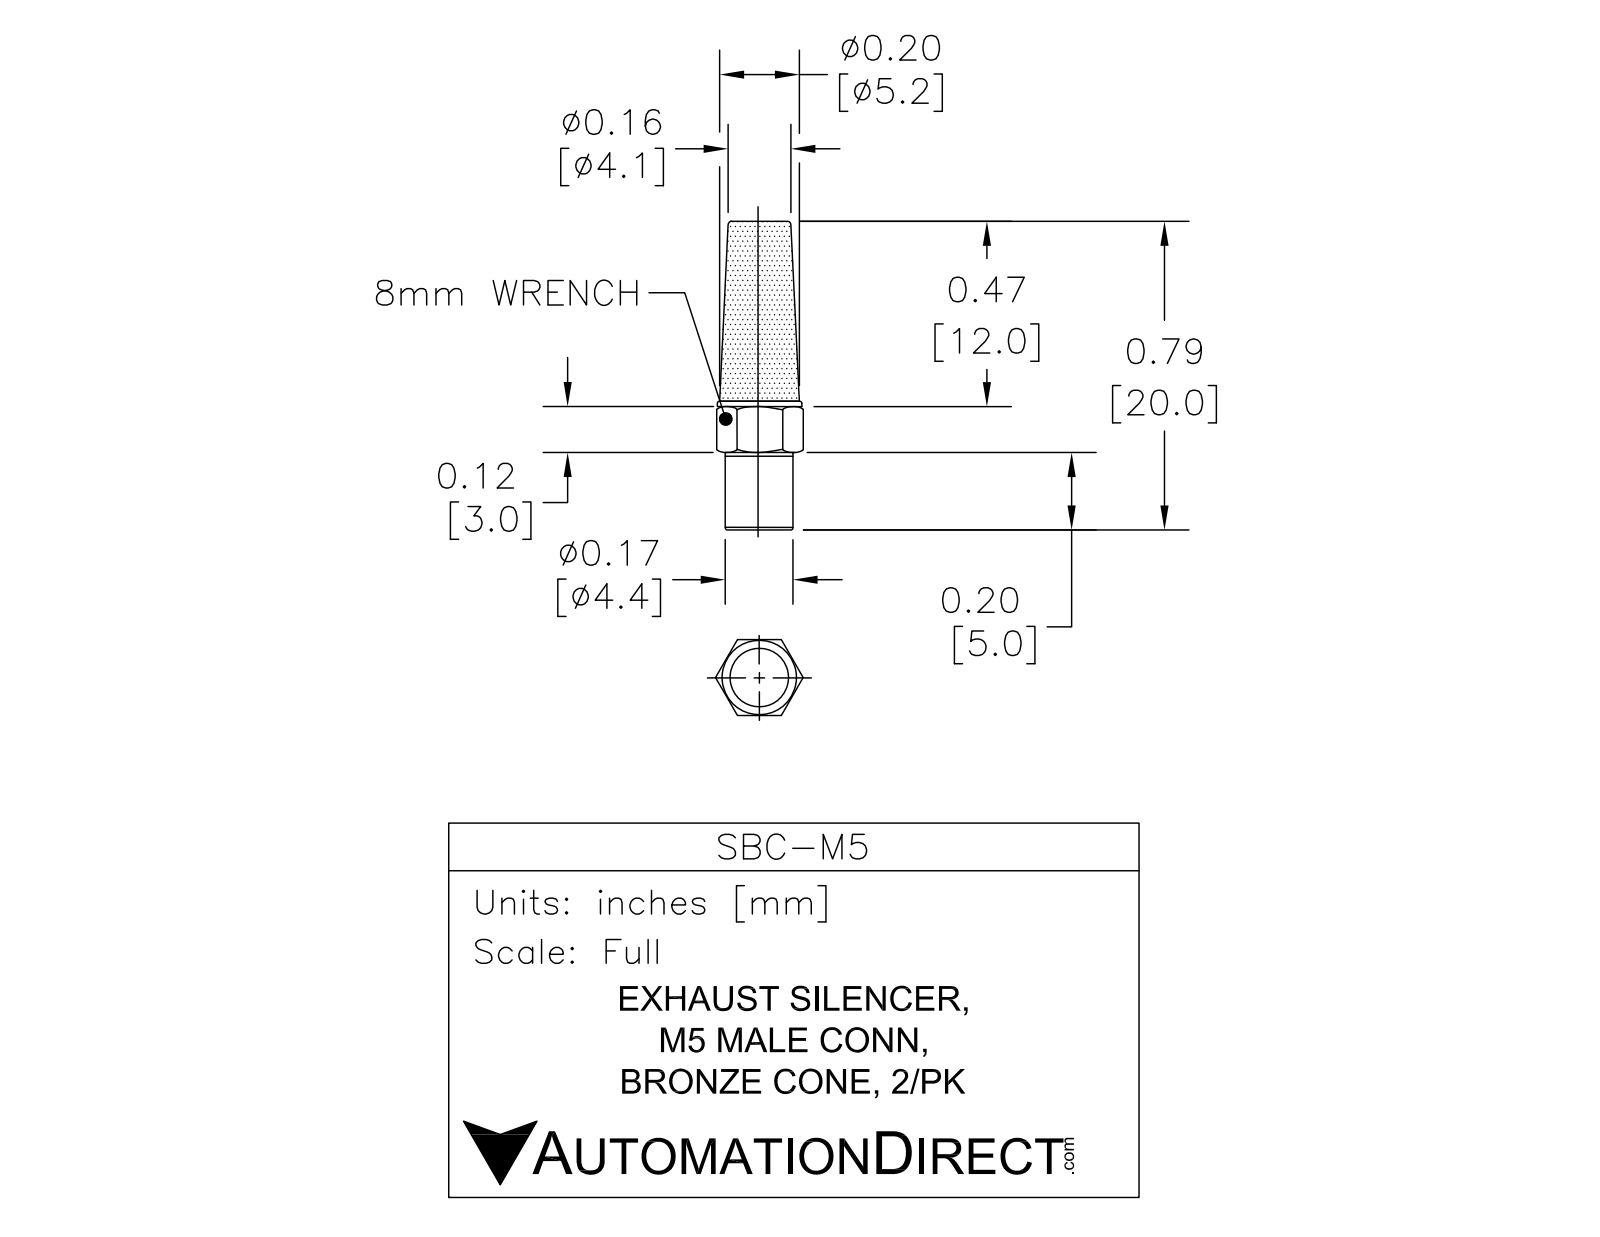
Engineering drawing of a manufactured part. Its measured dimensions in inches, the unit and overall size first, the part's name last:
Units: inches
Overall size (bounding box): 0.79 × 0.31 × 0.268
Round holes (diameter × count): ⌀0.125 ×1
Round bosses / shafts (diameter × count): ⌀0.23 ×1, ⌀0.196 ×1
Main face-to-face distances: 0.269, 0.12, 0.59, 0.47, 0.552, 0.431, 0.039, 0.2, 0.32, 0.752
Volume: 0.015 in³ · Surface area: 0.975 in²
Bodies: 1 solid, 55 faces (13 planar, 16 cylindrical, 26 other)
Part name (STEP PRODUCT): SBC-M5
STEP written by: SolidWorks 2015 (CONFIG_CONTROL_DESIGN)
